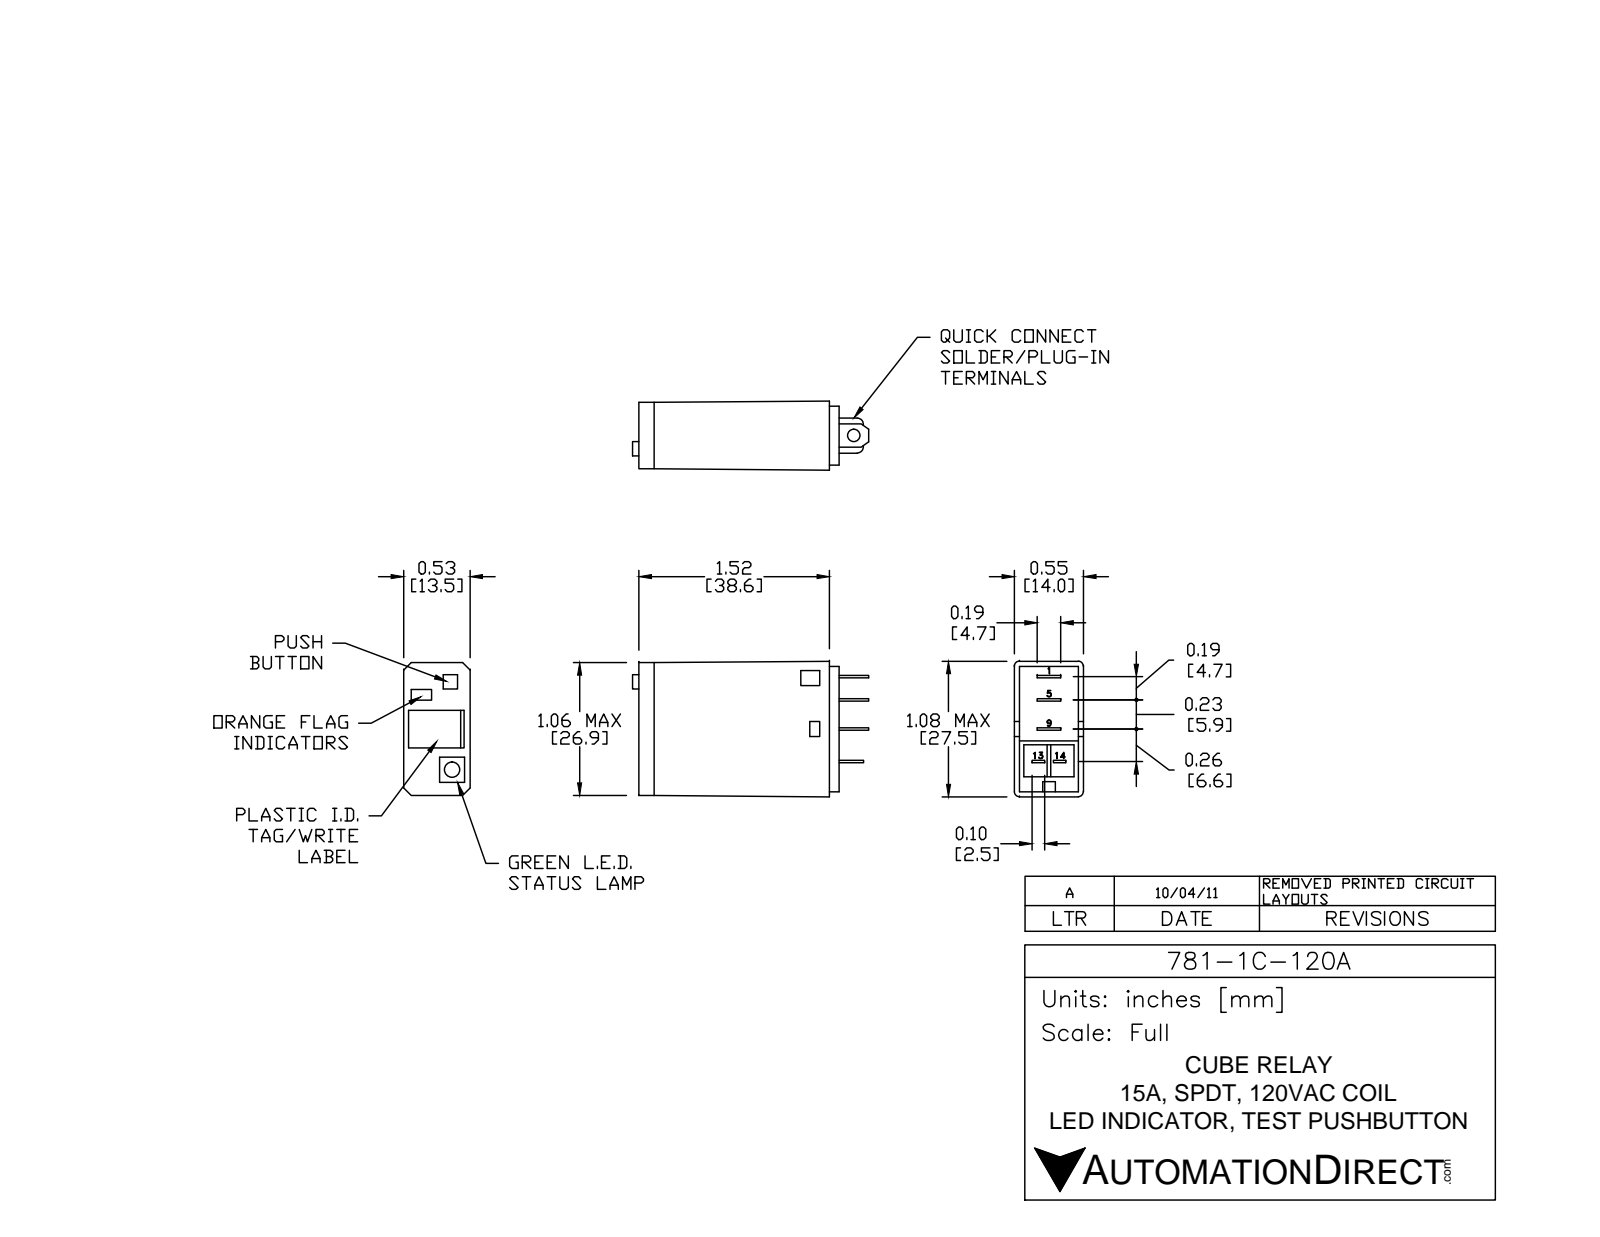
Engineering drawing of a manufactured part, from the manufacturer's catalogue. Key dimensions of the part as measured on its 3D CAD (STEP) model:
Part name (STEP PRODUCT): 781-1C-120A
STEP written by: SolidWorks 2021 (CONFIG_CONTROL_DESIGN)
Units: inches
Bodies: 1 solid, 124 faces (109 planar, 15 cylindrical, 0 other)
Overall size (bounding box): 1.86 × 1.1 × 0.53
Volume: 0.876 in³ · Surface area: 6.681 in²
Round holes (diameter × count): ⌀0.07 ×2, ⌀0.11 ×1, ⌀0.125 ×1
Partial cylindrical surfaces — rounded edges, fillets, slot ends (radius × count): R0.062 ×2, R0.155 ×1
Main face-to-face distances: 1.6, 0.02, 0.08, 0.185, 1.52, 0.19, 0.2, 0.195, 0.45, 1.515
Hole centre spacings: 0.08, 0.16
